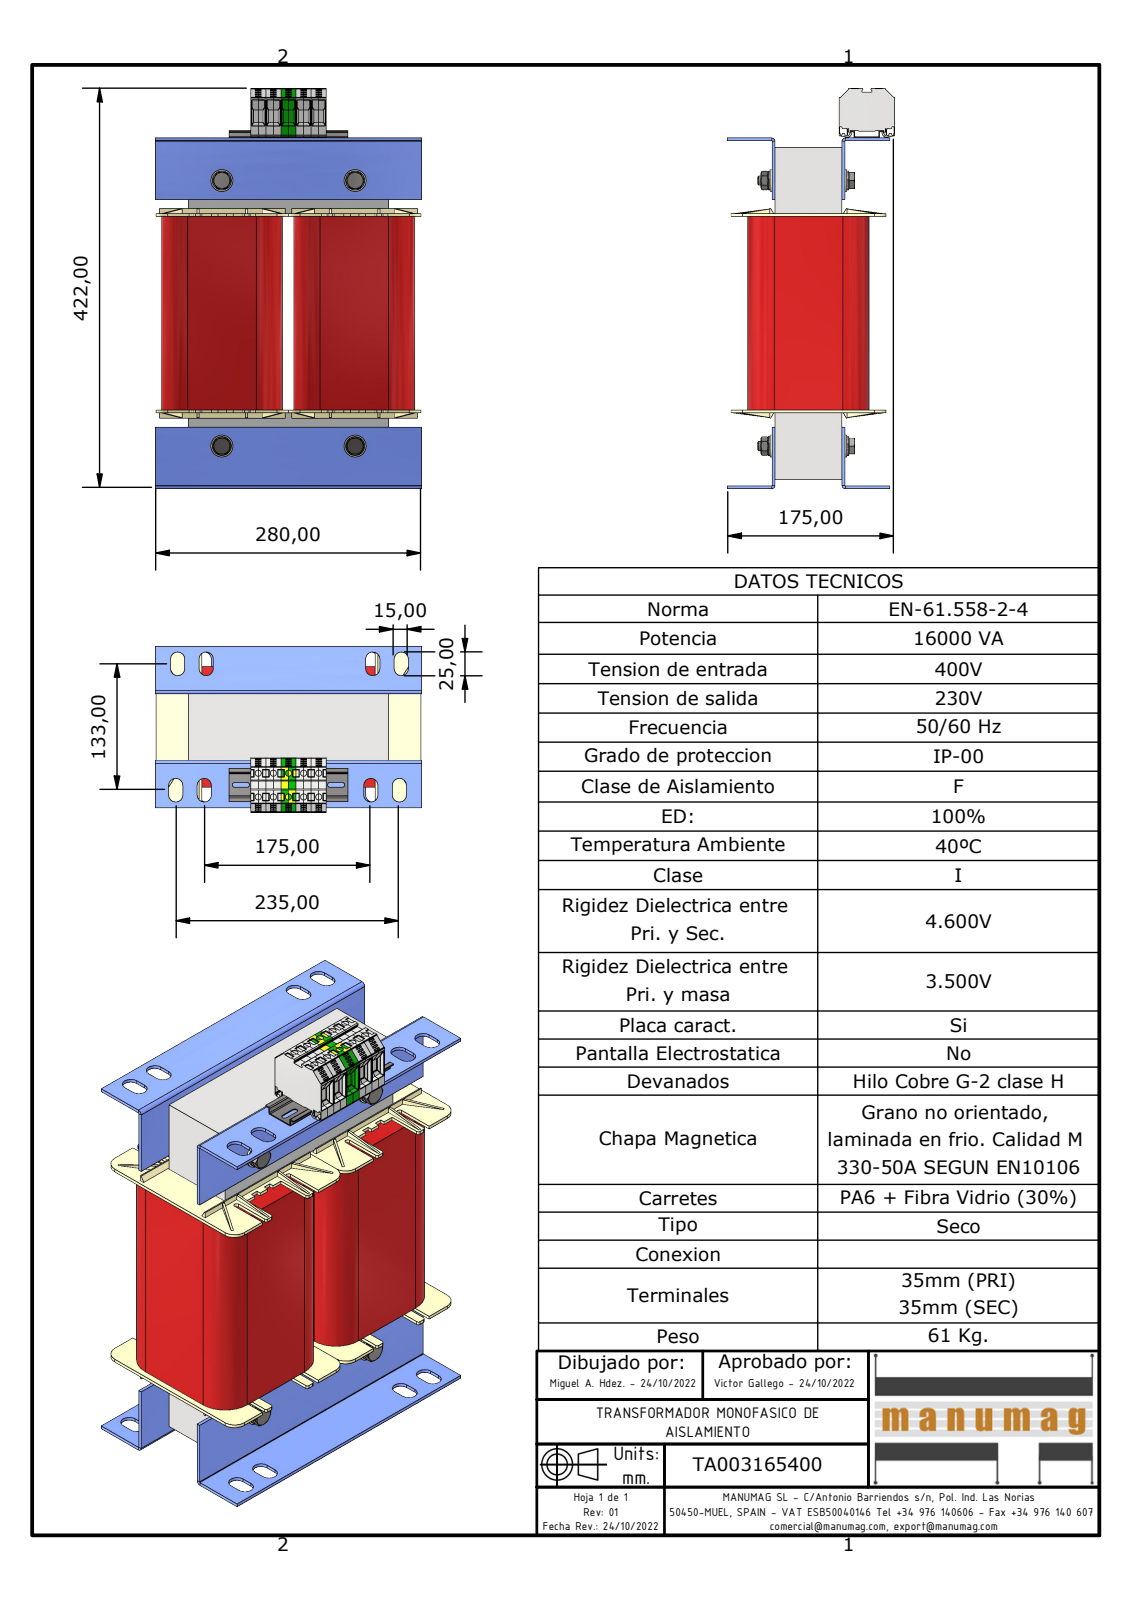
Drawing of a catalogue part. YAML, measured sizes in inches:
part_name: "TA003165400; UI350 x 210 - 70 (Rc70); RC 70 UI; UI 210_70_BOBINADO (+7 more)"
step_written_by: "Autodesk Inventor 2023 (AUTOMOTIVE_DESIGN)"
units: inches
bodies: {solids: 37, faces: 4574, planar: 2664, cylindrical: 1314, other: 596}
overall_size: [16.626, 11.024, 6.894]
volume: 553.7
surface_area: 1965
round_holes:
  - {diameter: 0.256, count: 10}
  - {diameter: 0.079, count: 4}
  - {diameter: 0.33, count: 4}
  - {diameter: 0.394, count: 4}
  - {diameter: 0.413, count: 4}
  - {diameter: 0.551, count: 4}
  - {diameter: 0.63, count: 4}
round_bosses_or_shafts:
  - {diameter: 0.906, count: 4}
  - {diameter: 0.787, count: 4}
  - {diameter: 0.606, count: 4}
  - {diameter: 0.453, count: 4}
  - {diameter: 0.362, count: 4}
partial_cylinders:
  - {radius: 0.012, count: 318}
  - {radius: 0.02, count: 136}
  - {radius: 0.295, count: 32}
  - {radius: 0.079, count: 26}
  - {radius: 0.039, count: 24}
  - {radius: 0.01, count: 18}
  - {radius: 0.098, count: 16}
  - {radius: 0.102, count: 10}
face_to_face_distances: [0.118, 2.874, 2.756, 0.02, 2.894, 0.138, 5.472, 1.004, 1.122, 3.878]
hole_center_spacings: [0.626, 1.167, 1.252, 1.593, 0.984, 1.878, 2.12, 0.313]
